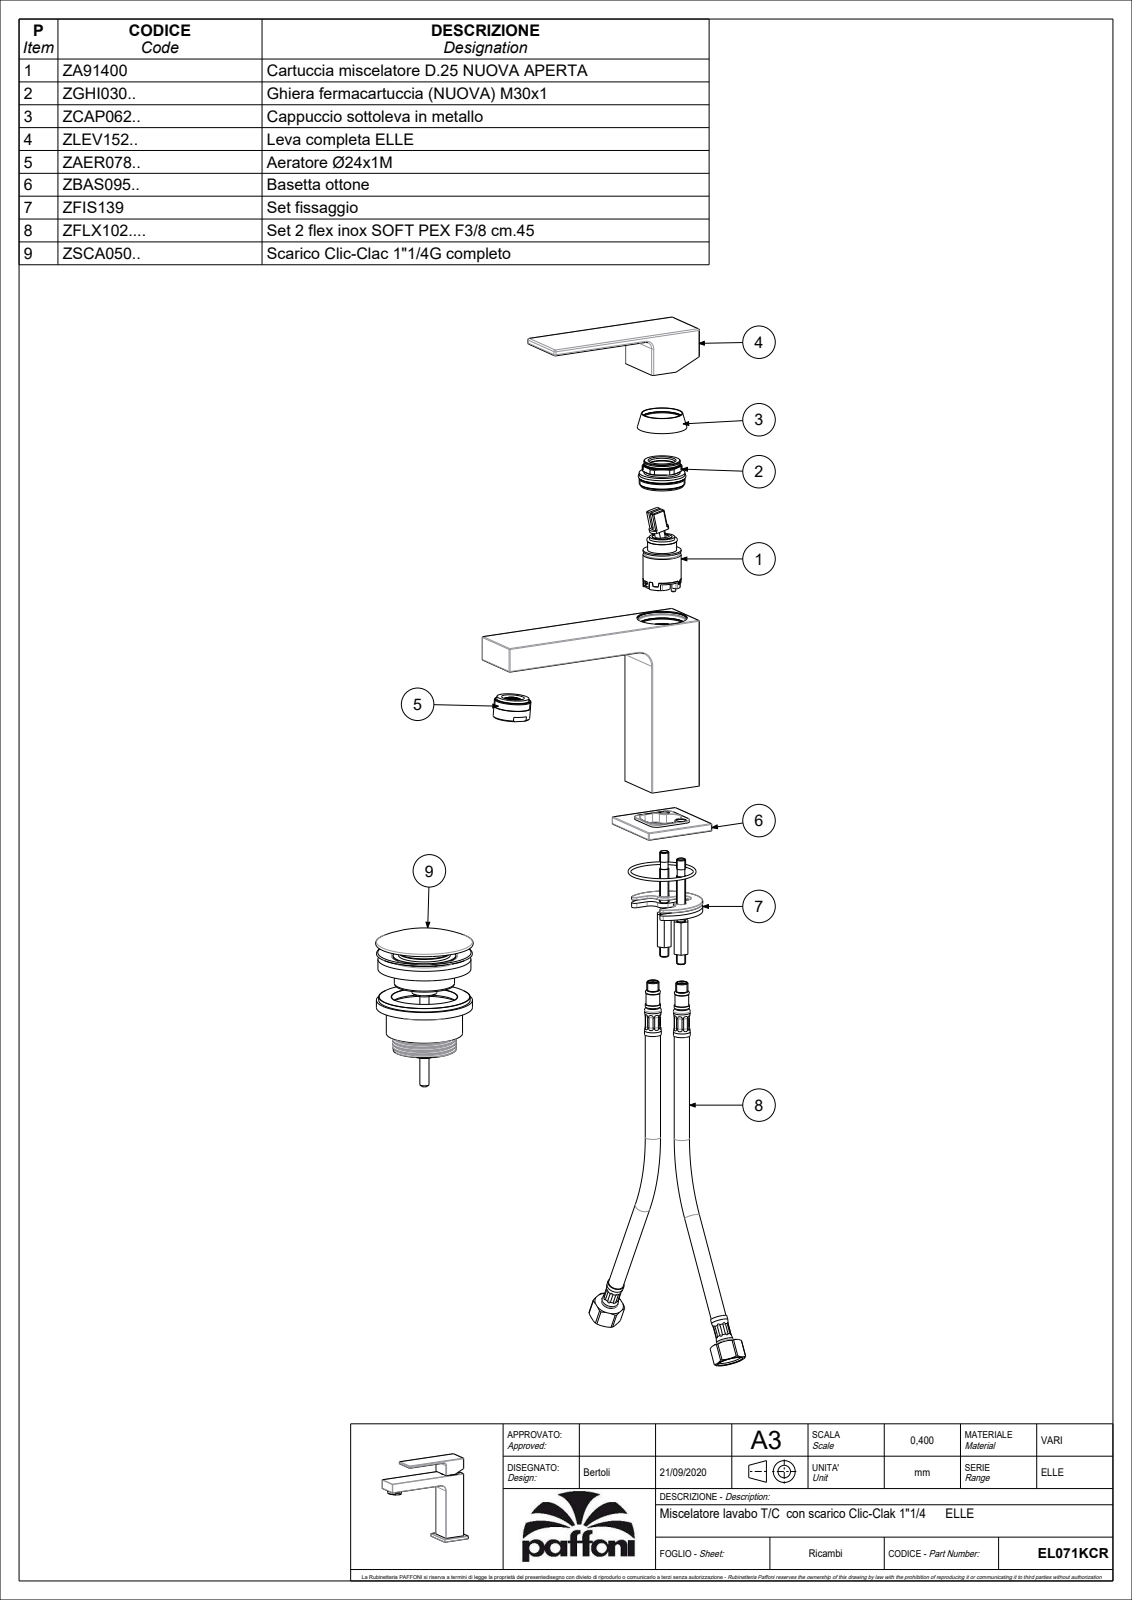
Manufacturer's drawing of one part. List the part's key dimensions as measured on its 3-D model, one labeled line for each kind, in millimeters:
Part name (STEP PRODUCT): EL071CR
STEP written by: CREO PARAMETRIC BY PTC INC, 2020044 (CONFIG_CONTROL_DESIGN)
Units: millimetres
Bodies: 2 solids, 173 faces (55 planar, 70 cylindrical, 48 other)
Overall size (bounding box): 150 × 145.58 × 48
Volume: 250 436 mm³ · Surface area: 49 943 mm²
Round holes (diameter × count): ⌀3 ×1, ⌀4.5 ×1, ⌀5.5 ×1, ⌀24.8 ×1, ⌀26.2 ×1, ⌀28 ×1
Round bosses / shafts (diameter × count): ⌀24 ×1
Partial cylindrical surfaces — rounded edges, fillets, slot ends (radius × count): R0.5 ×25, R1 ×13, R1.5 ×8, R5 ×1, R10.5 ×1
Main face-to-face distances: 36, 28.08, 16, 44.08, 40.08, 24.08, 4, 101.5, 117.5, 141.58
